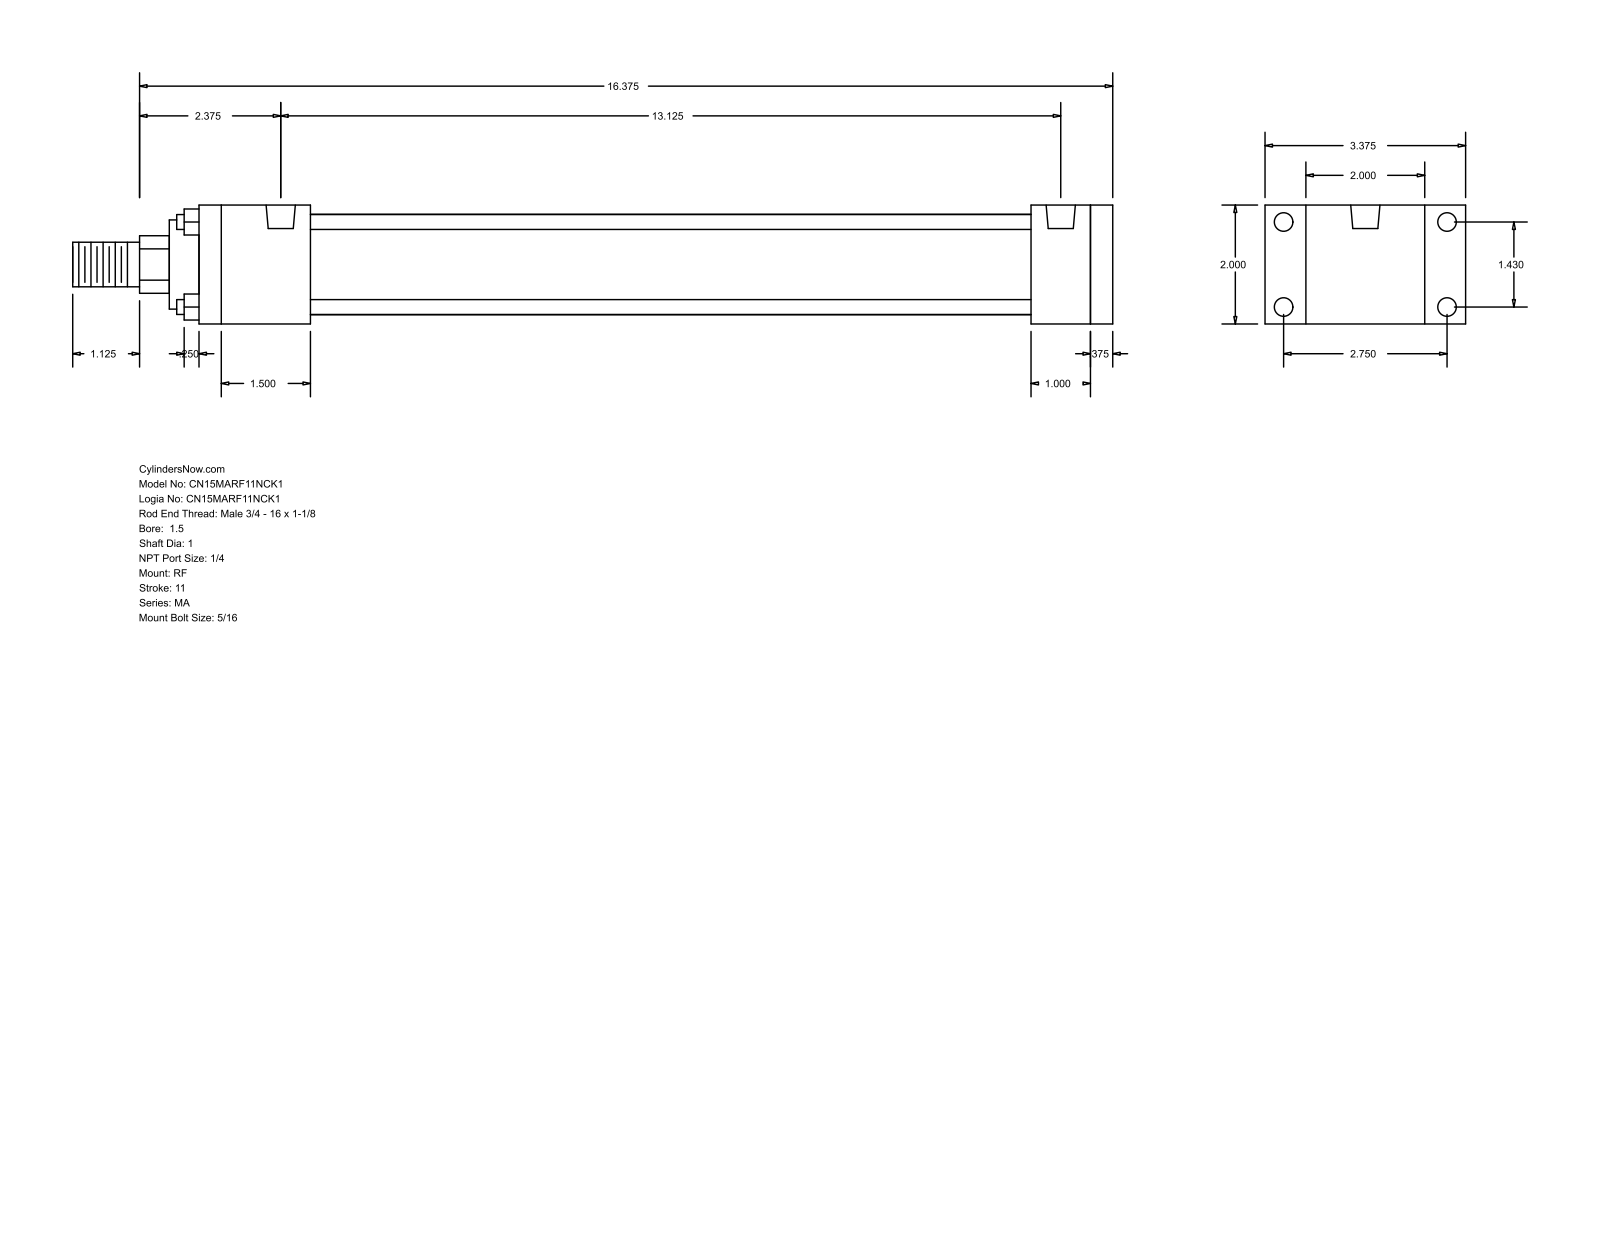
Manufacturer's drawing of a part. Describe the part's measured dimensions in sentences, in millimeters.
The part is named "MA_RF__0150_1". Its 3-D file was written by "GSSL Pune (CONFIG_CONTROL_DESIGN)". It is 0 solids with 92 faces: 64 planar, 28 cylindrical and 0 other. Overall it measures 444.5 by 85.72 by 50.8 millimeters. Round holes: 8 of diameter 7.94, 2 of diameter 12.49. Round bosses or shafts: 4 of diameter 6.35, 1 of diameter 42.93, 1 of diameter 38.1, 1 of diameter 25.4, 1 of diameter 19.05. Partial cylindrical surfaces (rounded edges, fillets, slot ends): 1 of radius 12.29. The main face-to-face distances are 50.8, 9.53, 381, 25.4, 390.53, 355.6, 34.93, 47.63, 307.97, 333.37. The hole center spacings are 36.32, 69.84, 78.72, 333.37.
